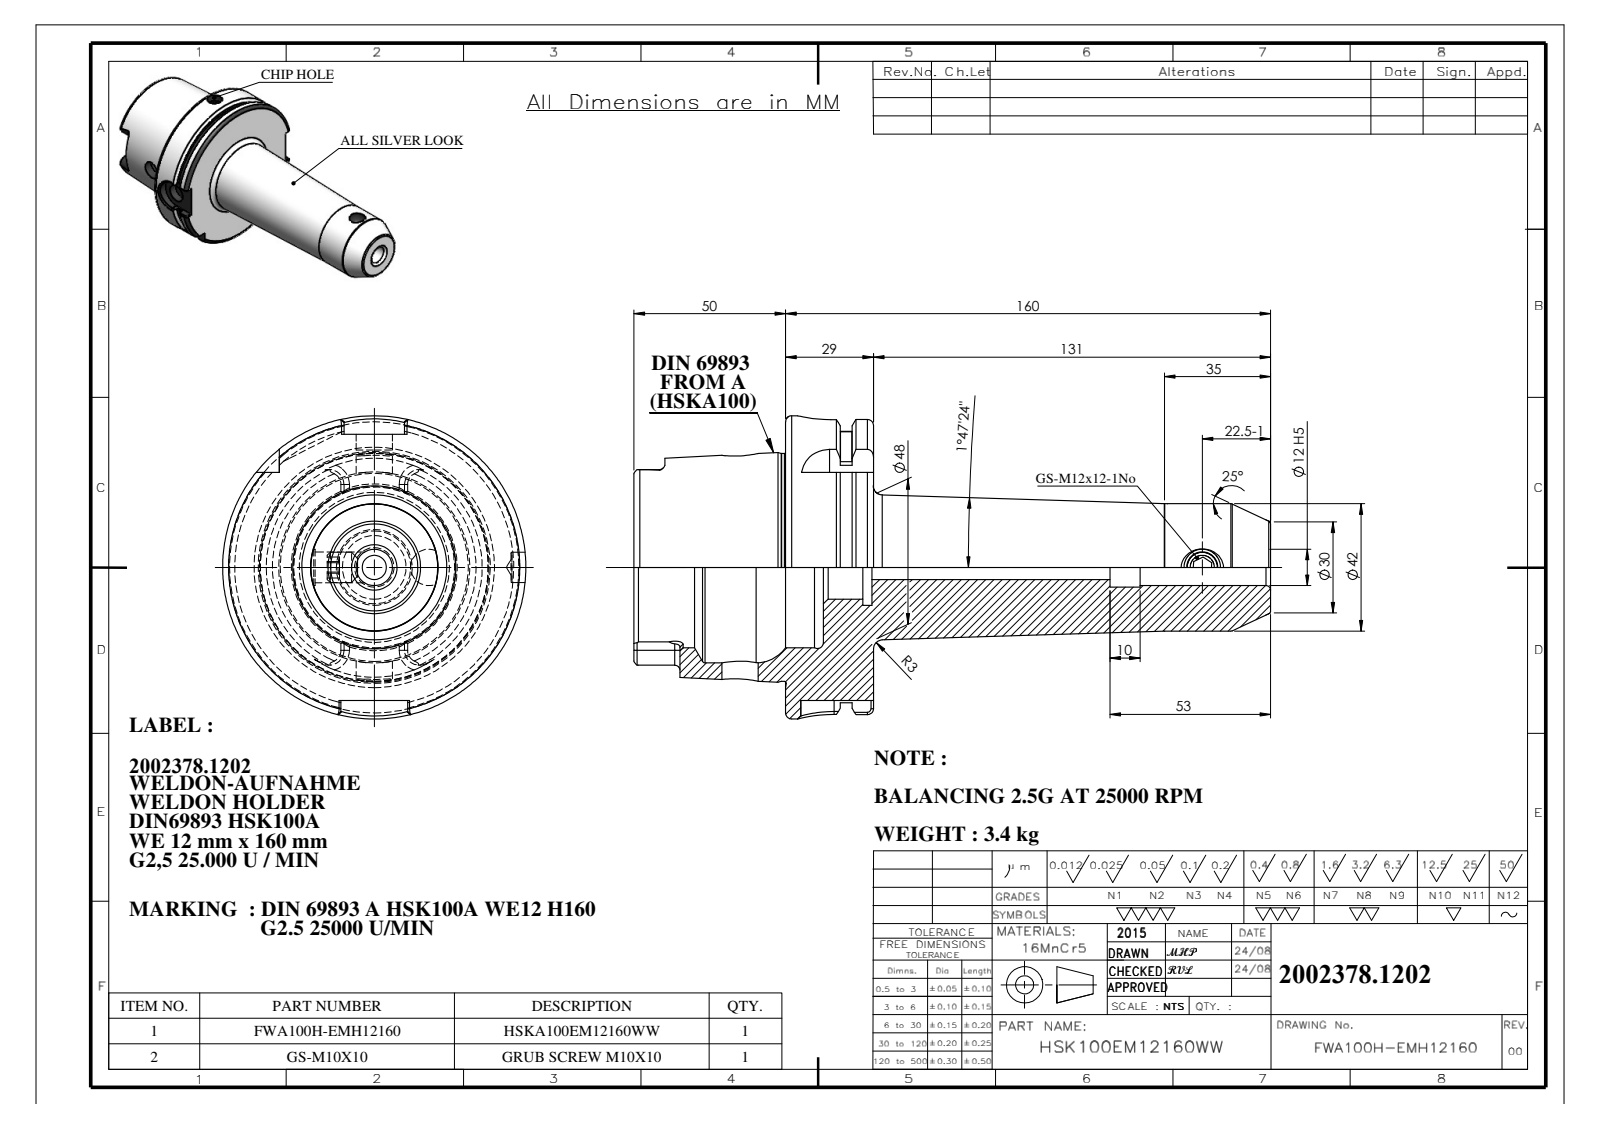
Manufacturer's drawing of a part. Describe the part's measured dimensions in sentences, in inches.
The part is named "HSKA100EM12160WW; M10X10; 91100A-WE812160". Its 3-D file was written by "SolidWorks 2018 (CONFIG_CONTROL_DESIGN)". It is 2 solids with 206 faces: 64 planar, 58 cylindrical and 84 other. Overall it measures 8.268 by 3.937 by 3.937 inches. Its volume is 26.79 cubic inches and its surface area 110.8 square inches. Round holes: 4 of diameter 0.472, 1 of diameter 0.315, 1 of diameter 0.394, 1 of diameter 0.402, 1 of diameter 0.512, 1 of diameter 0.827, 1 of diameter 0.984, 1 of diameter 2.087, 1 of diameter 2.48. Round bosses or shafts: 1 of diameter 3.937, 1 of diameter 3.622, 1 of diameter 2.959, 1 of diameter 1.654, 1 of diameter 0.394. Partial cylindrical surfaces (rounded edges, fillets, slot ends): 6 of radius 0.071, 4 of radius 0.192, 2 of radius 0.394, 1 of radius 0.433. The main face-to-face distances are 1.142, 0.65, 0.492, 1.969, 2.461, 3.11, 3.091, 0.02, 8.268, 6.299. The hole center spacings are 1.181, 5.138.
